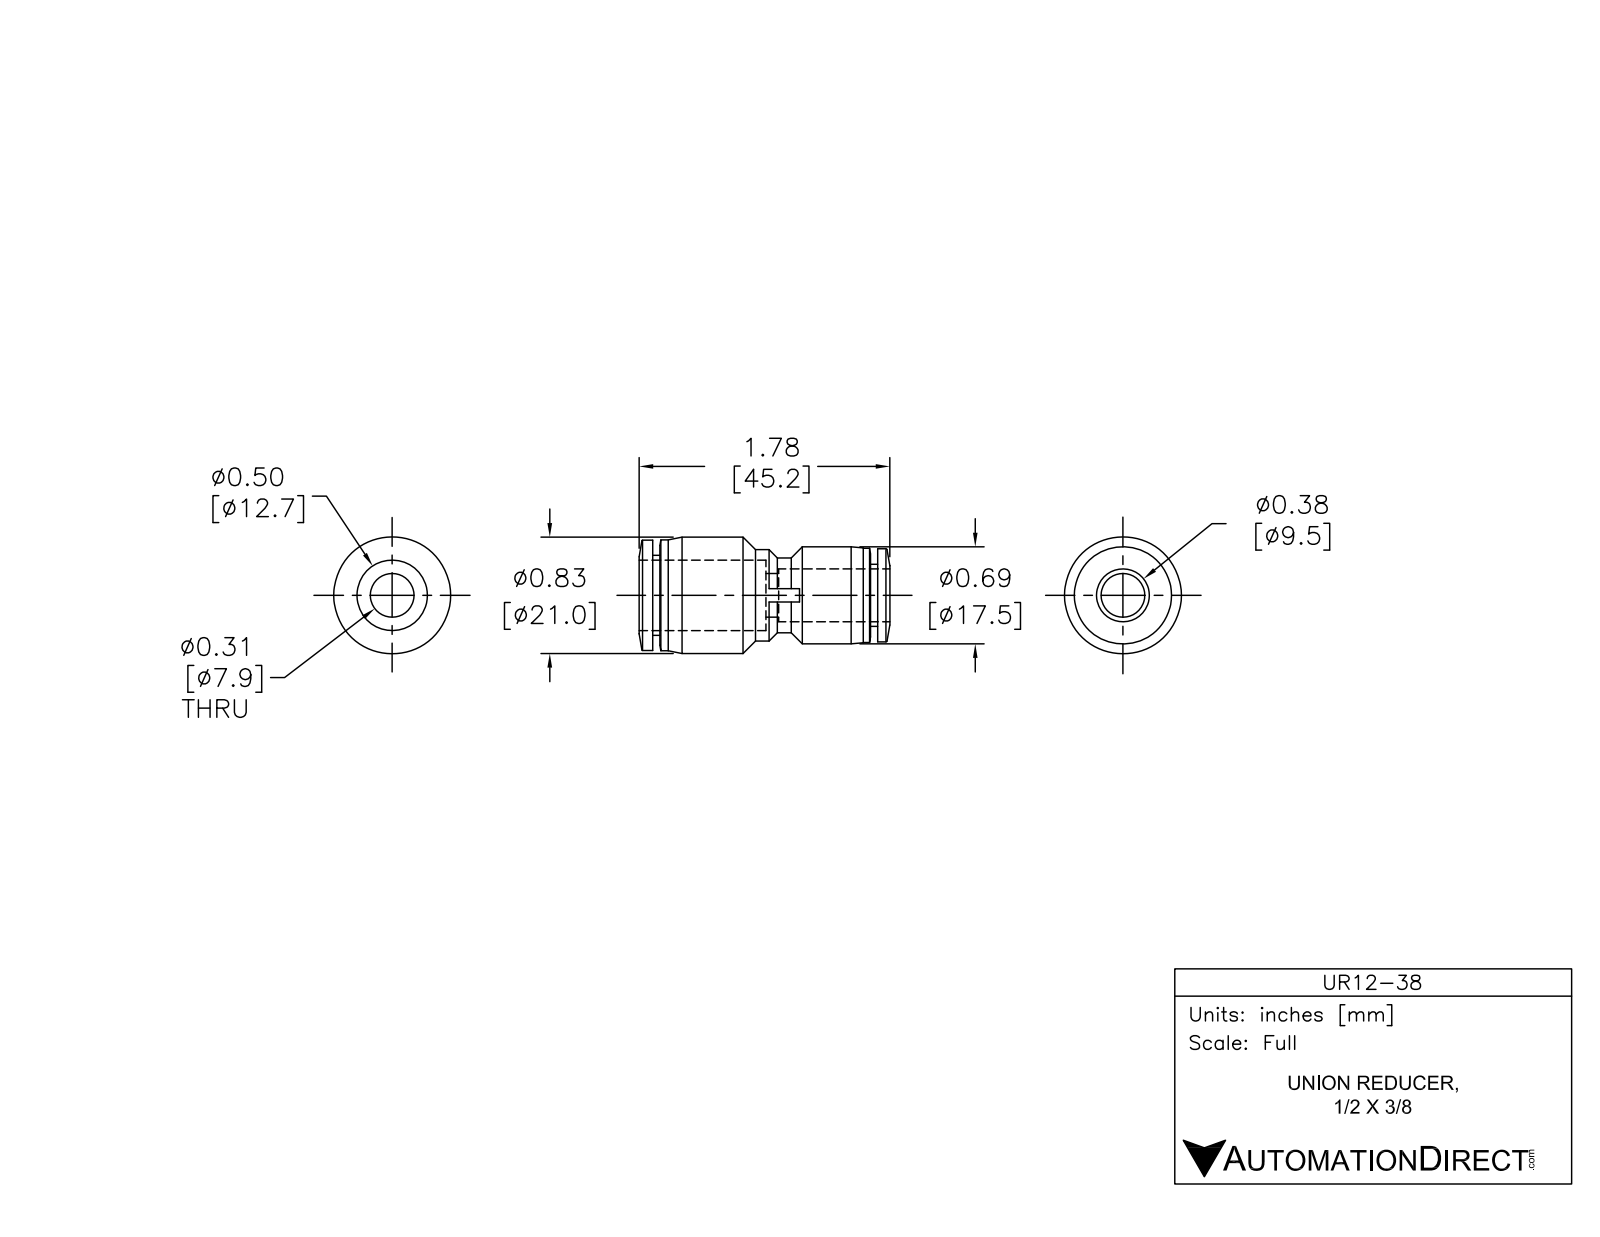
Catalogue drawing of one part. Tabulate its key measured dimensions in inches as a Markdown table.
| quantity | value |
| --- | --- |
| part name | UR12-38 |
| STEP written by | SolidWorks 2015 (AUTOMOTIVE_DESIGN) |
| units | inches |
| bodies | 1 solid, 67 faces (11 planar, 26 cylindrical, 30 other) |
| overall size | 1.781 × 0.827 × 0.827 |
| volume | 0.43 in³ |
| surface area | 8.067 in² |
| round holes (diameter × count) | 0.315 × 1, 0.386 × 1, 0.51 × 1 |
| round bosses / shafts (diameter × count) | 0.827 × 1, 0.787 × 1, 0.783 × 1, 0.689 × 1, 0.669 × 1, 0.661 × 1, 0.65 × 1, 0.569 × 1 |
| main face-to-face distances | 0.051, 1.547, 1.598, 0.785, 0.762, 0.813, 1.496, 0.734, 0.705, 0.654 |
